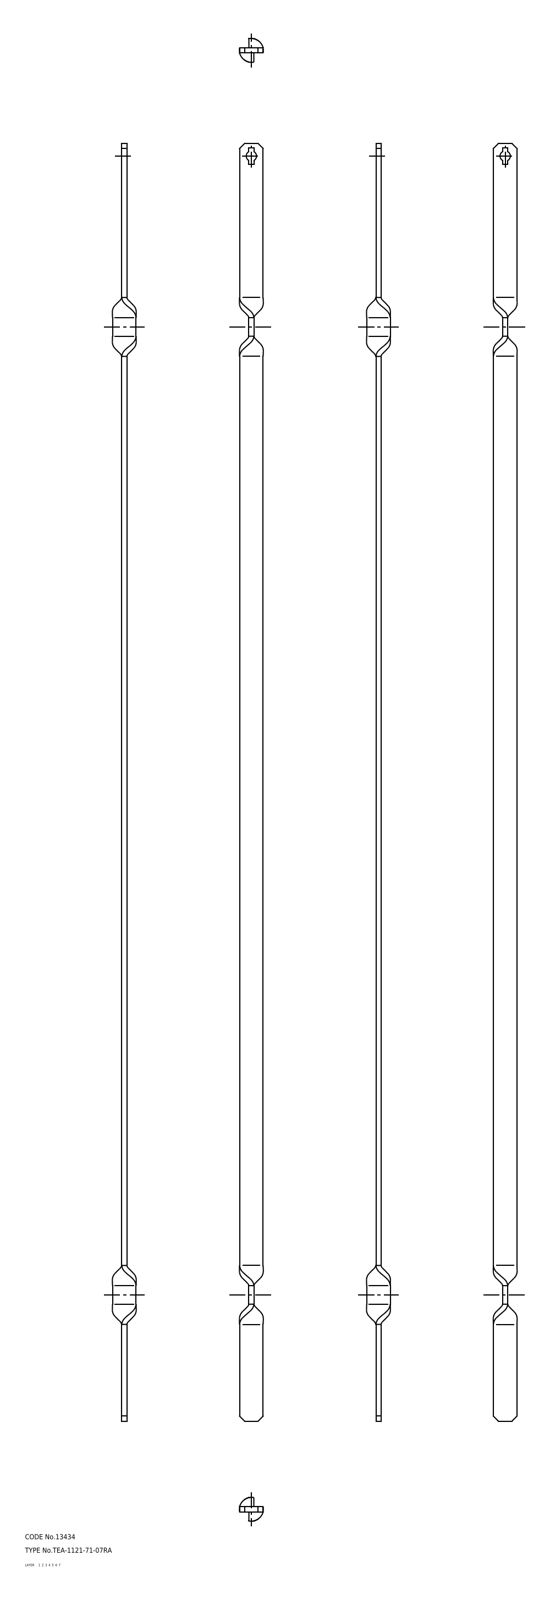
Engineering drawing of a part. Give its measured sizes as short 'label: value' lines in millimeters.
name: rod
written by: CADfix (AUTOMOTIVE_DESIGN)
unit: mm
bodies: 1 solid, 34 faces (0 planar, 0 cylindrical, 34 other)
size: 759 × 14.2 × 14.18
volume: 31 692 mm³; area: 26 010 mm²
